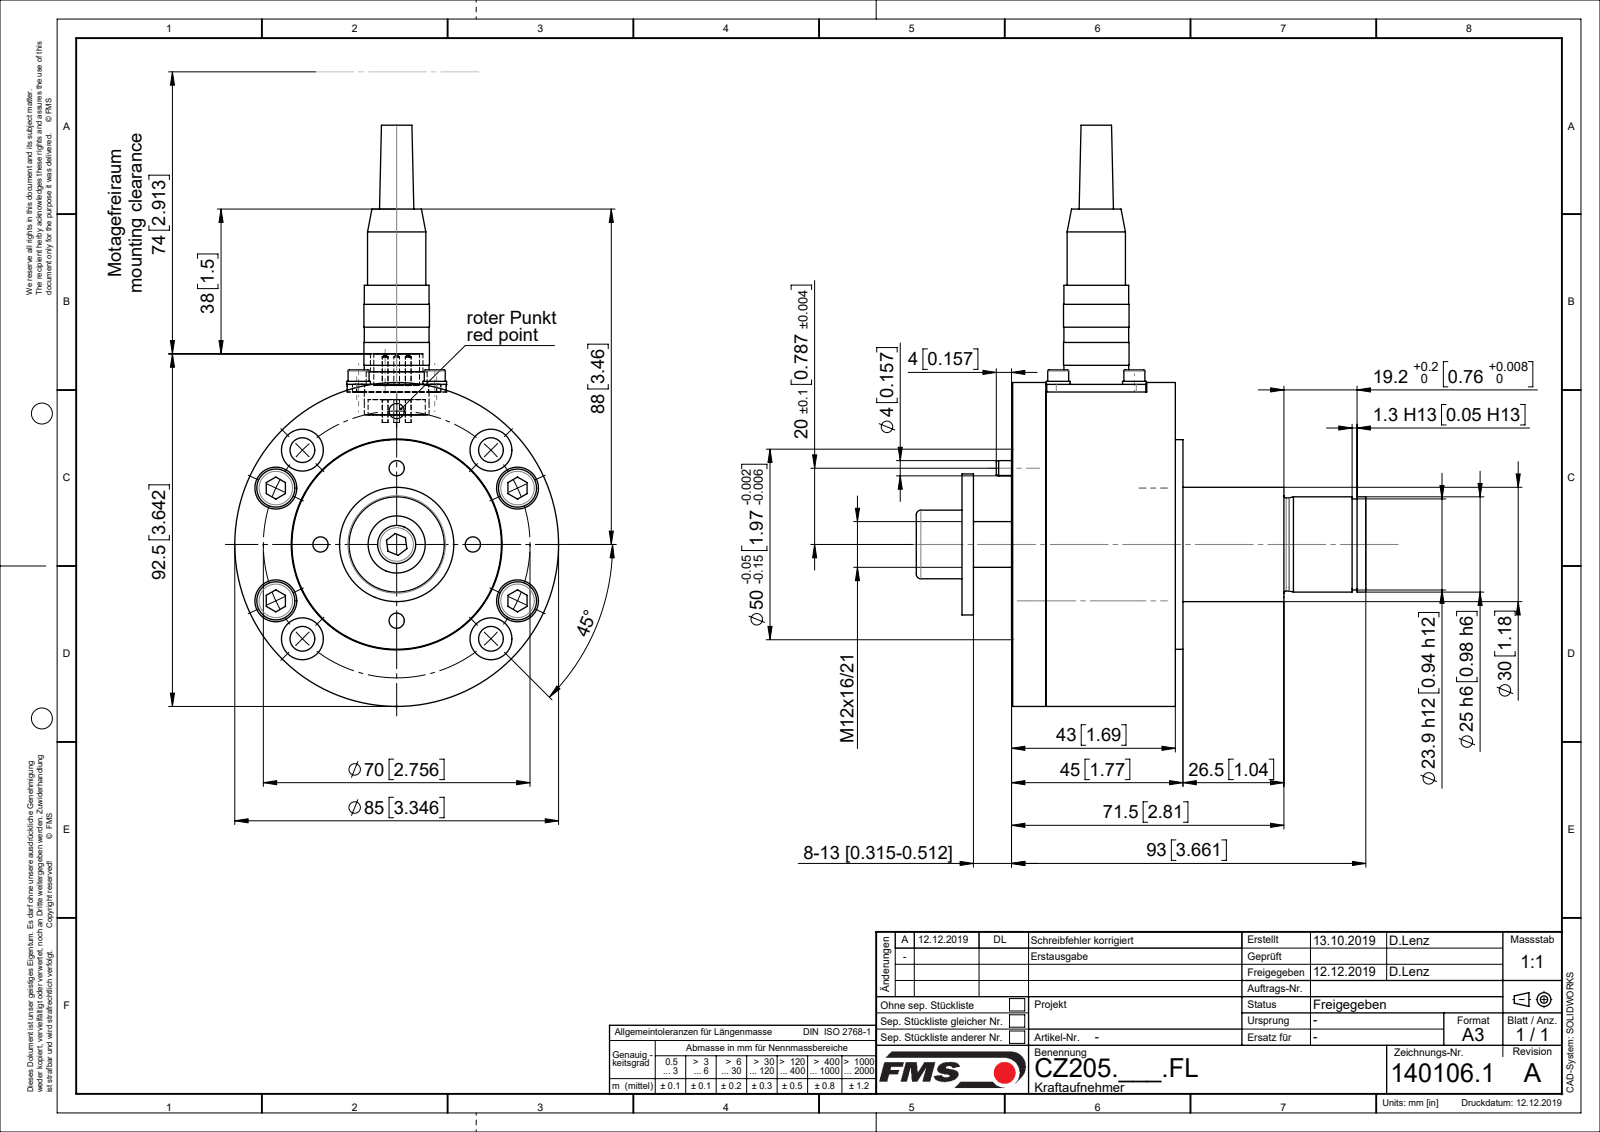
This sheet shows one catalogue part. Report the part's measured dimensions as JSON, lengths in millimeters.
{"part_name": "ZEICHNUNG2; C1401061; C0709081; C0612056 (+8 more)", "step_written_by": "Mechanical Desktop 2009 (CONFIG_CONTROL_DESIGN)", "units": "millimeters", "bodies": {"solids": 26, "faces": 487, "planar": 156, "cylindrical": 245, "other": 86}, "overall_size": [152.5, 119, 85], "volume_mm3": 237791, "surface_area_mm2": 85093, "round_holes": [[6.5, 8], [11, 8], [2.6, 4], [3.2, 4], [4, 4], [5.15, 4], [7, 4], [15, 2], [7.15, 1], [9, 1], [10.68, 1], [12, 1]], "round_bosses_or_shafts": [[1.5, 5], [10, 4], [6.2, 4], [6, 4], [5.5, 4], [5, 4], [3, 4], [85, 1]], "partial_cylinders_radius": [[2.5, 4], [5, 2]], "face_to_face_distances": [45, 10, 2, 8.7, 42.7, 34, 16, 44.7, 36, 33.5], "hole_center_spacings": [20, 25.2, 35, 51.14, 28.28, 12.16, 14.14, 18.87]}
